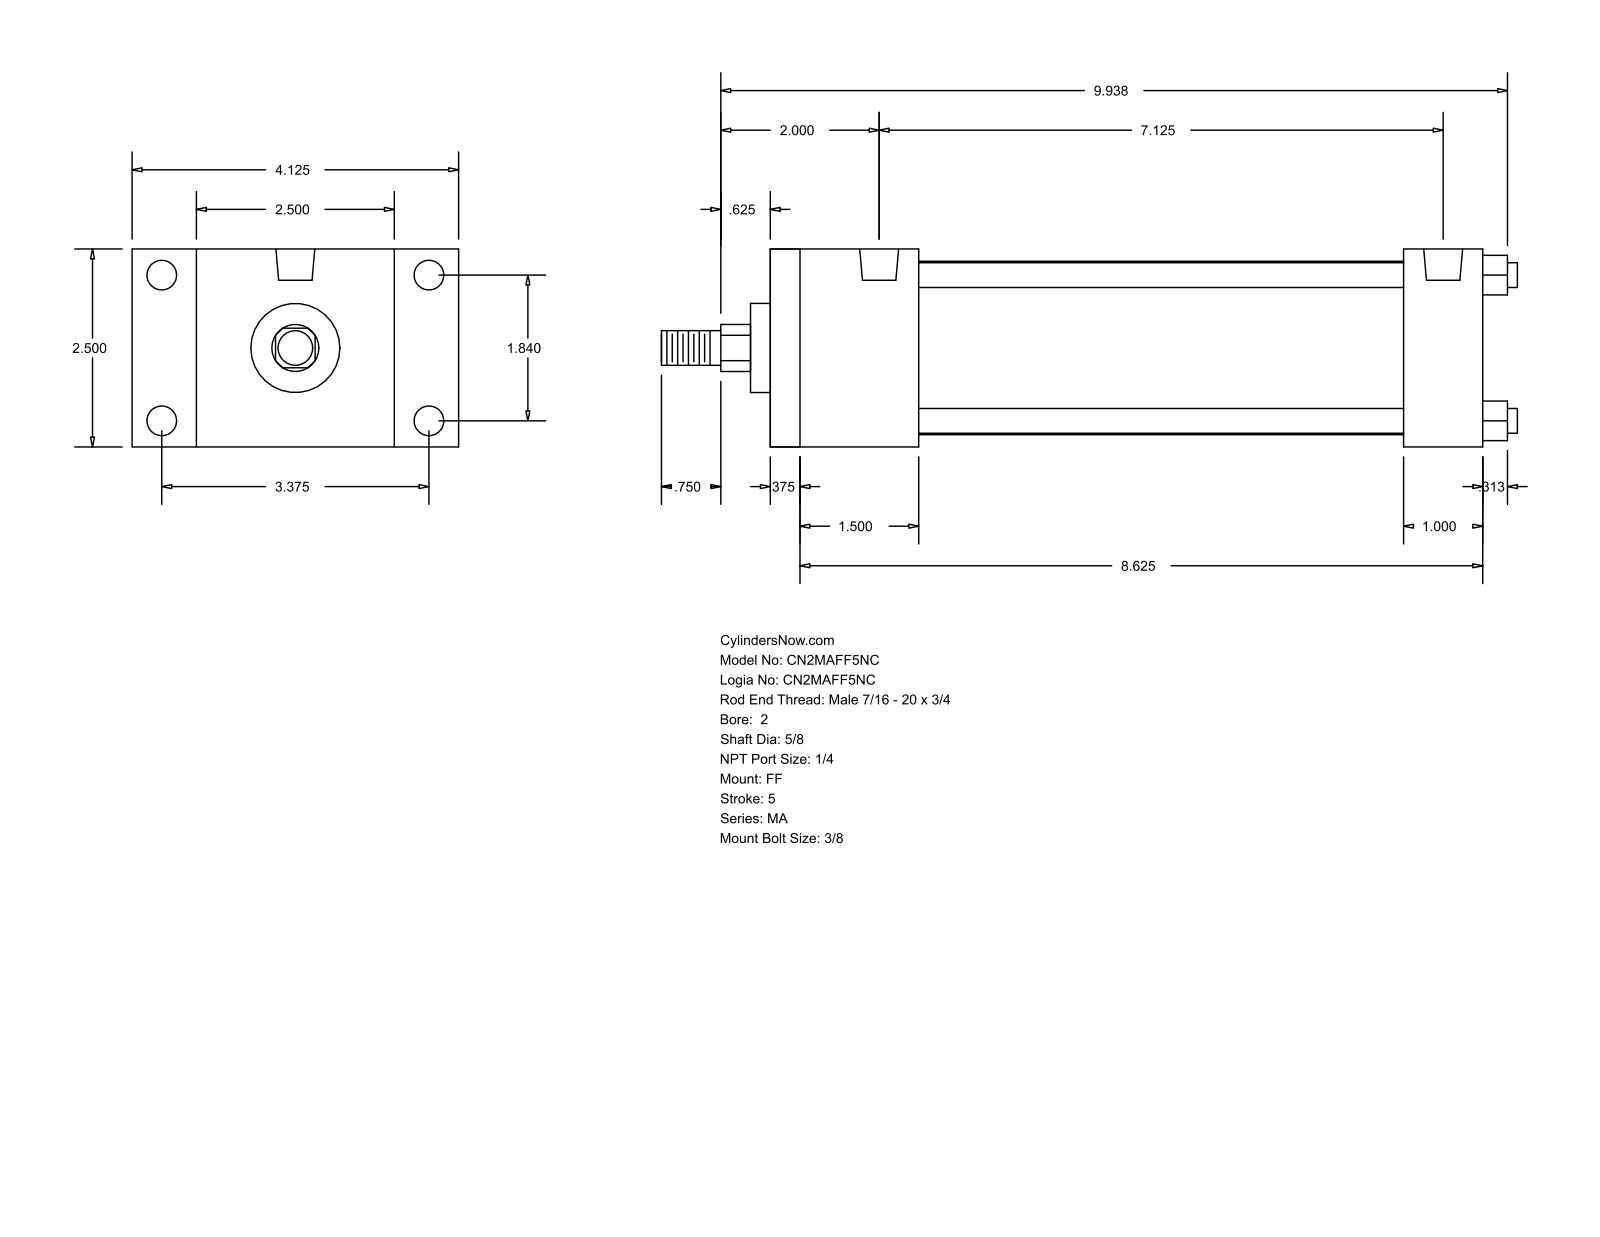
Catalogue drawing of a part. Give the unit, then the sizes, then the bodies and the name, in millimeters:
Units: millimetres
Overall size (bounding box): 274.64 × 104.78 × 63.5
Round holes (diameter × count): ⌀7.94 ×4, ⌀9.53 ×4, ⌀12.49 ×2
Round bosses / shafts (diameter × count): ⌀7.94 ×4, ⌀55.63 ×1, ⌀28.57 ×1, ⌀15.88 ×1, ⌀11.11 ×1
Partial cylindrical surfaces — rounded edges, fillets, slot ends (radius × count): R7.54 ×1
Main face-to-face distances: 63.5, 228.59, 219.07, 9.52, 25.4, 38.1, 47.62, 203.19, 193.67, 155.57
Hole centre spacings: 46.74, 85.72, 97.63, 180.98
Bodies: 0 solids, 92 faces (64 planar, 28 cylindrical, 0 other)
Part name (STEP PRODUCT): MA_FF__0200_0.625
STEP written by: GSSL Pune (CONFIG_CONTROL_DESIGN)
